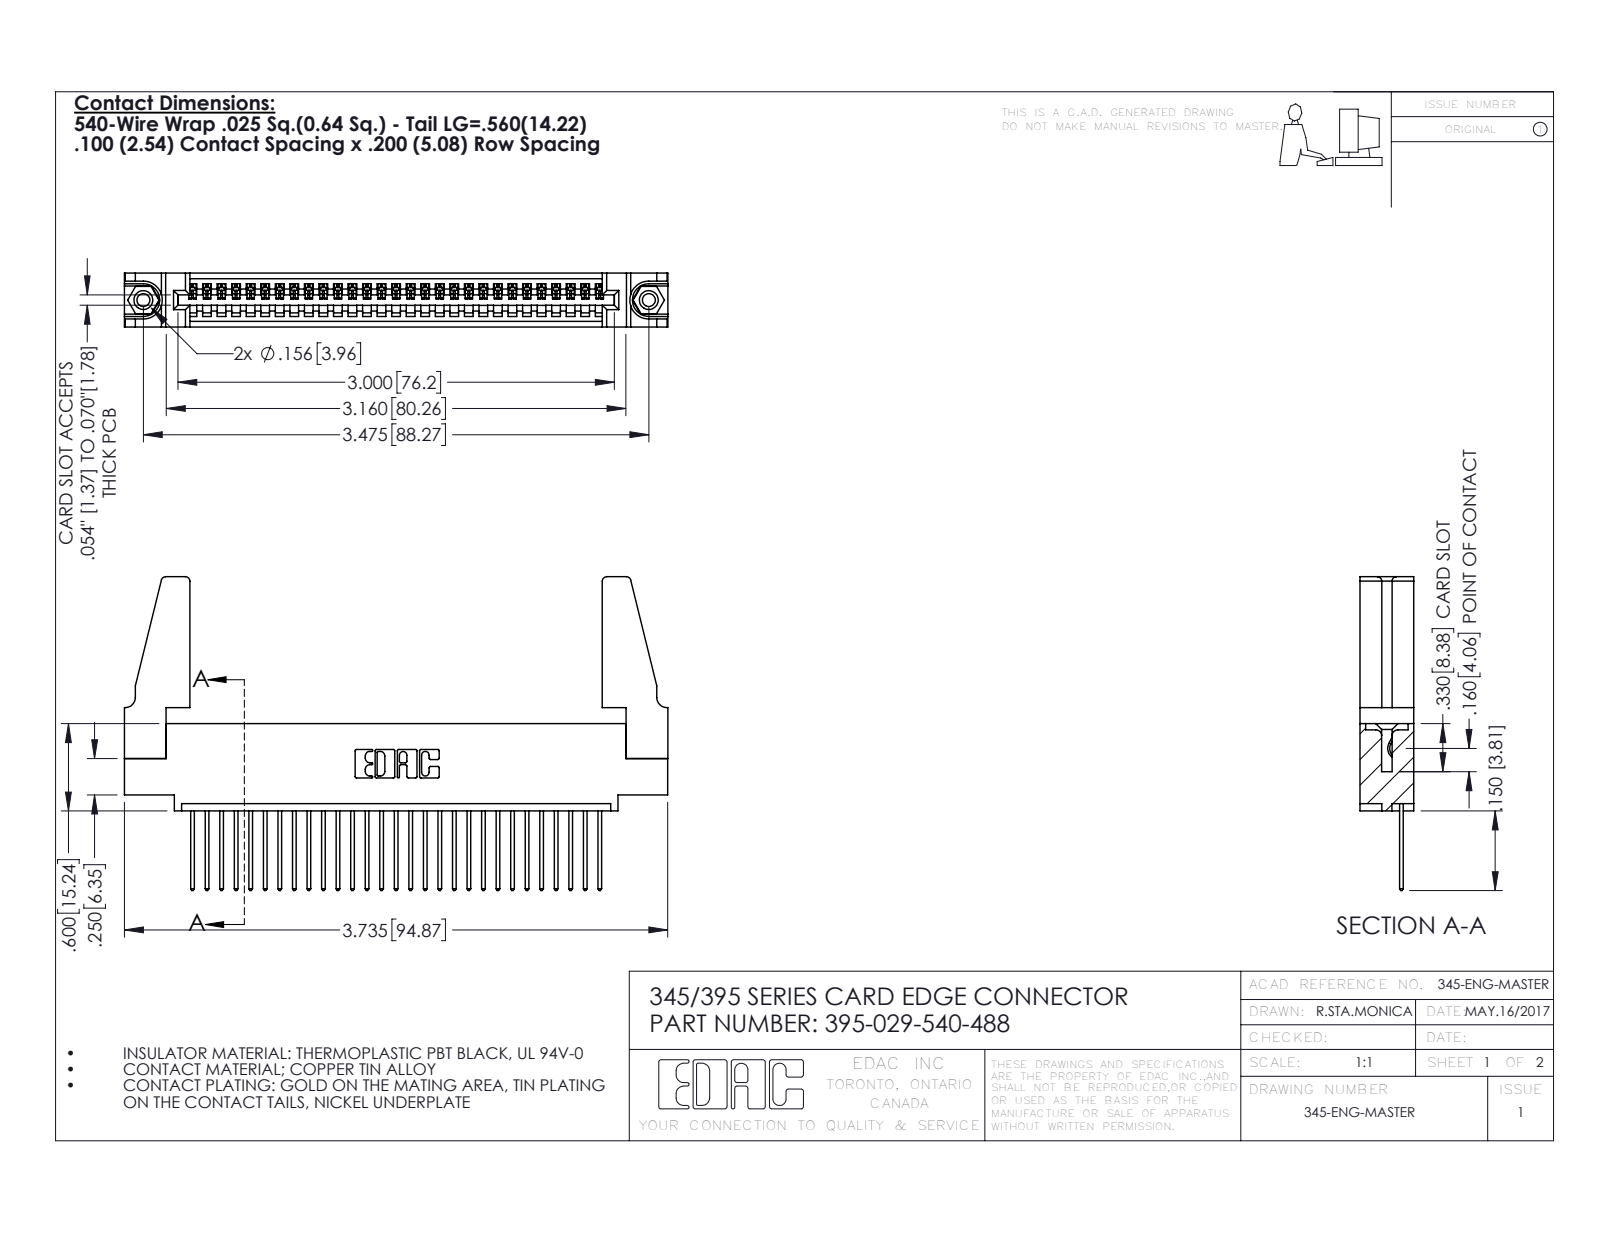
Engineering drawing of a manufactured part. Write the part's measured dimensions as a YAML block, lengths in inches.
part_name: "345-220-078_345-220-088; 345 Part_0.110 Offset - 0.156 Dia-TH; 395-029-540-488; 345-250-001_345-250-001-102 (+1 more)"
step_written_by: "SolidWorks 2016 (CONFIG_CONTROL_DESIGN)"
units: inches
bodies: {solids: 34, faces: 1936, planar: 1316, cylindrical: 604, other: 16}
overall_size: [3.736, 2.157, 0.37]
volume: 0.74
surface_area: 23.42
round_holes:
  - {diameter: 0.089, count: 2}
  - {diameter: 0.125, count: 2}
  - {diameter: 0.156, count: 2}
  - {diameter: 0.064, count: 1}
round_bosses_or_shafts:
  - {diameter: 0.155, count: 2}
partial_cylinders:
  - {radius: 0.006, count: 58}
  - {radius: 0.01, count: 58}
  - {radius: 0.01, count: 22}
  - {radius: 0.03, count: 8}
  - {radius: 0.007, count: 6}
  - {radius: 0.031, count: 6}
  - {radius: 0.026, count: 3}
  - {radius: 0.031, count: 2}
face_to_face_distances: [0.072, 0.298, 0.37, 0.098, 0.272, 0.025, 0.2, 0.225, 0.149, 0.072]
hole_center_spacings: [0.27, 3.24, 3.475]
